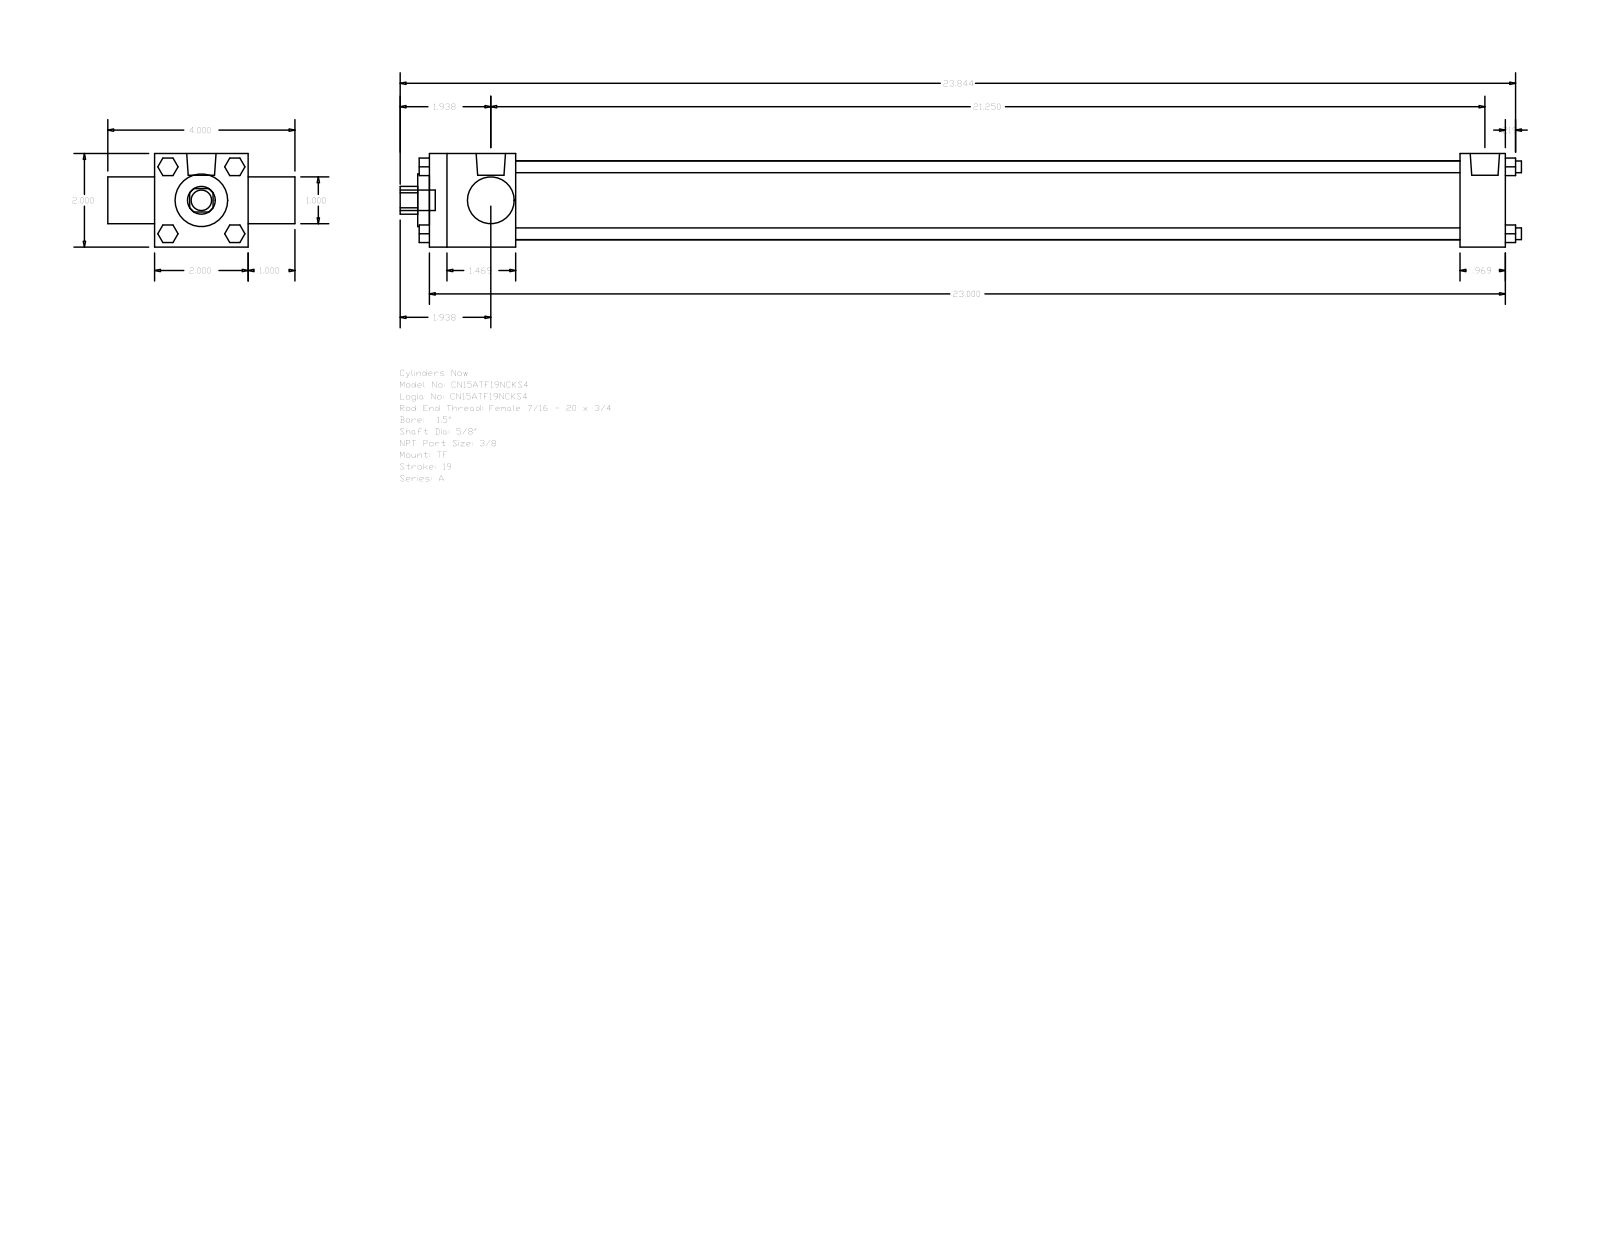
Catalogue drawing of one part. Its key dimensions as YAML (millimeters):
part_name: "A_TF__0150_0.625"
step_written_by: "GSSL Pune (CONFIG_CONTROL_DESIGN)"
units: millimeters
bodies: {solids: 0, faces: 120, planar: 92, cylindrical: 28, other: 0}
overall_size: [608.81, 101.6, 50.8]
round_holes:
  - {diameter: 15.88, count: 1}
  - {diameter: 25.4, count: 1}
  - {diameter: 28.57, count: 1}
  - {diameter: 42.93, count: 1}
round_bosses_or_shafts:
  - {diameter: 6.35, count: 4}
  - {diameter: 5.56, count: 3}
  - {diameter: 15.93, count: 2}
  - {diameter: 11.11, count: 1}
partial_cylinders:
  - {radius: 7.54, count: 1}
face_to_face_distances: [50.8, 584.2, 25.4, 76.2, 46.83, 559.59, 512.76, 537.37, 24.61, 9.52]
